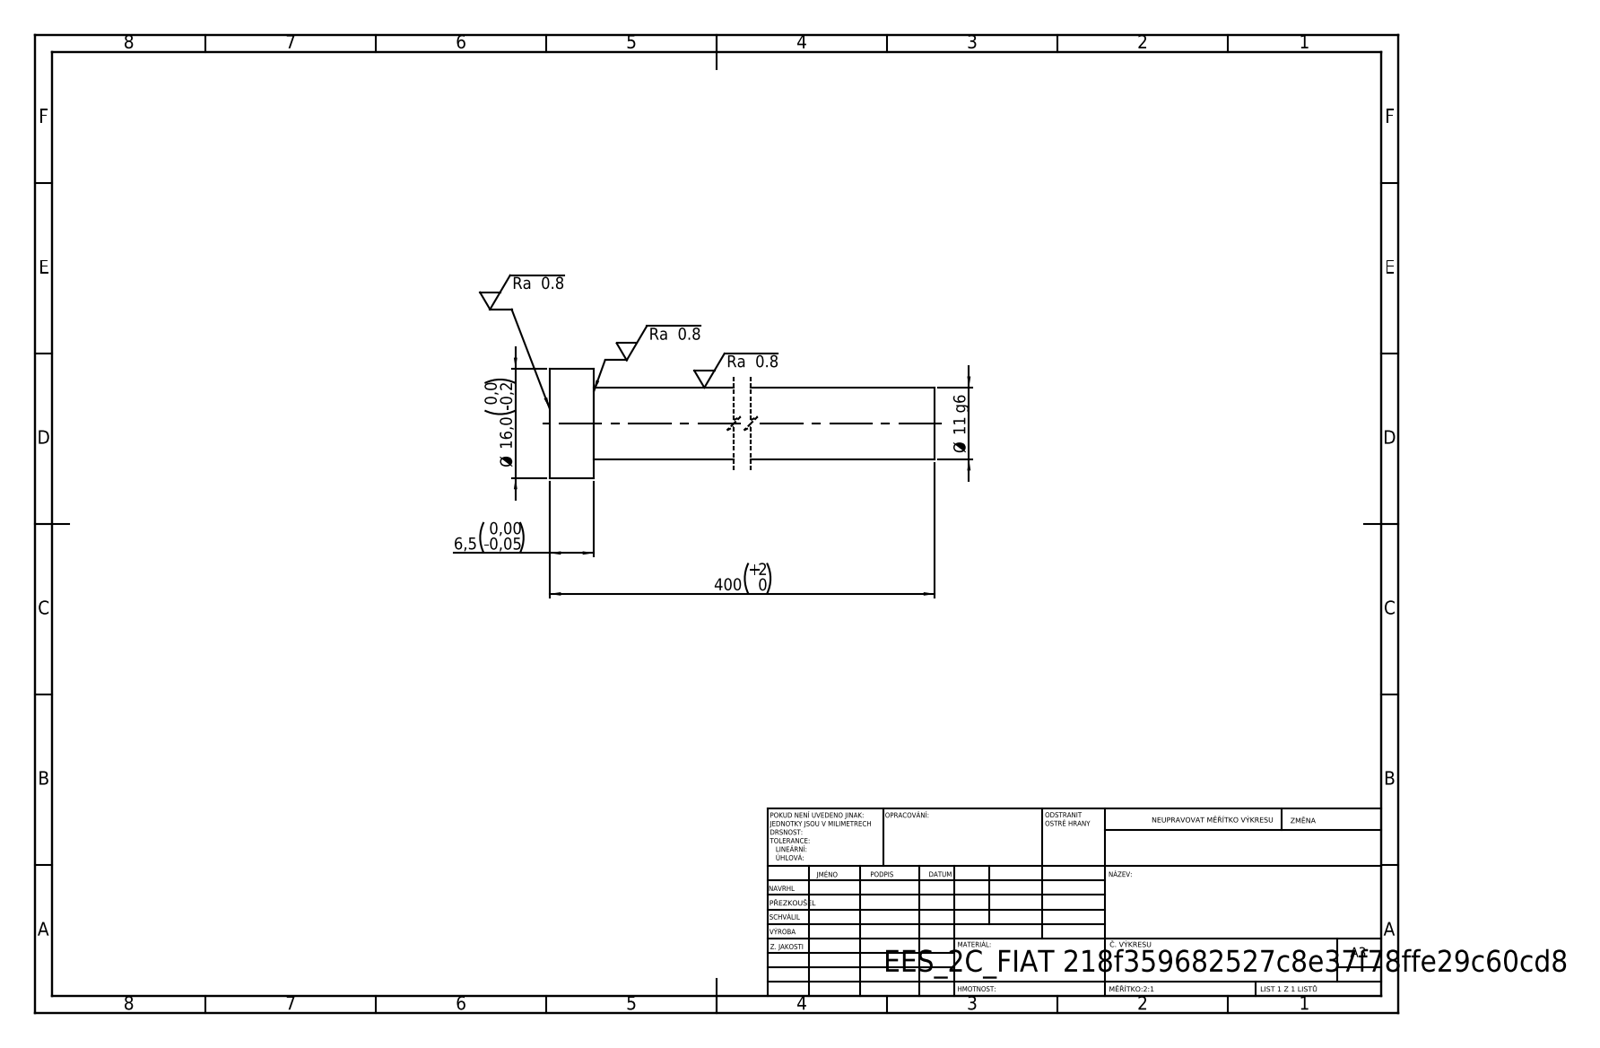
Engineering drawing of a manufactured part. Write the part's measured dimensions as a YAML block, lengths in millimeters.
step_written_by: "SolidWorks 2019 (CONFIG_CONTROL_DESIGN)"
units: millimeters
bodies: {solids: 1, faces: 7, planar: 3, cylindrical: 4, other: 0}
overall_size: [400, 16, 16]
volume: 35380
surface_area: 13709
round_bosses_or_shafts:
  - {diameter: 16, count: 1}
  - {diameter: 10.5, count: 1}
face_to_face_distances: [6.5, 400, 393.5]
